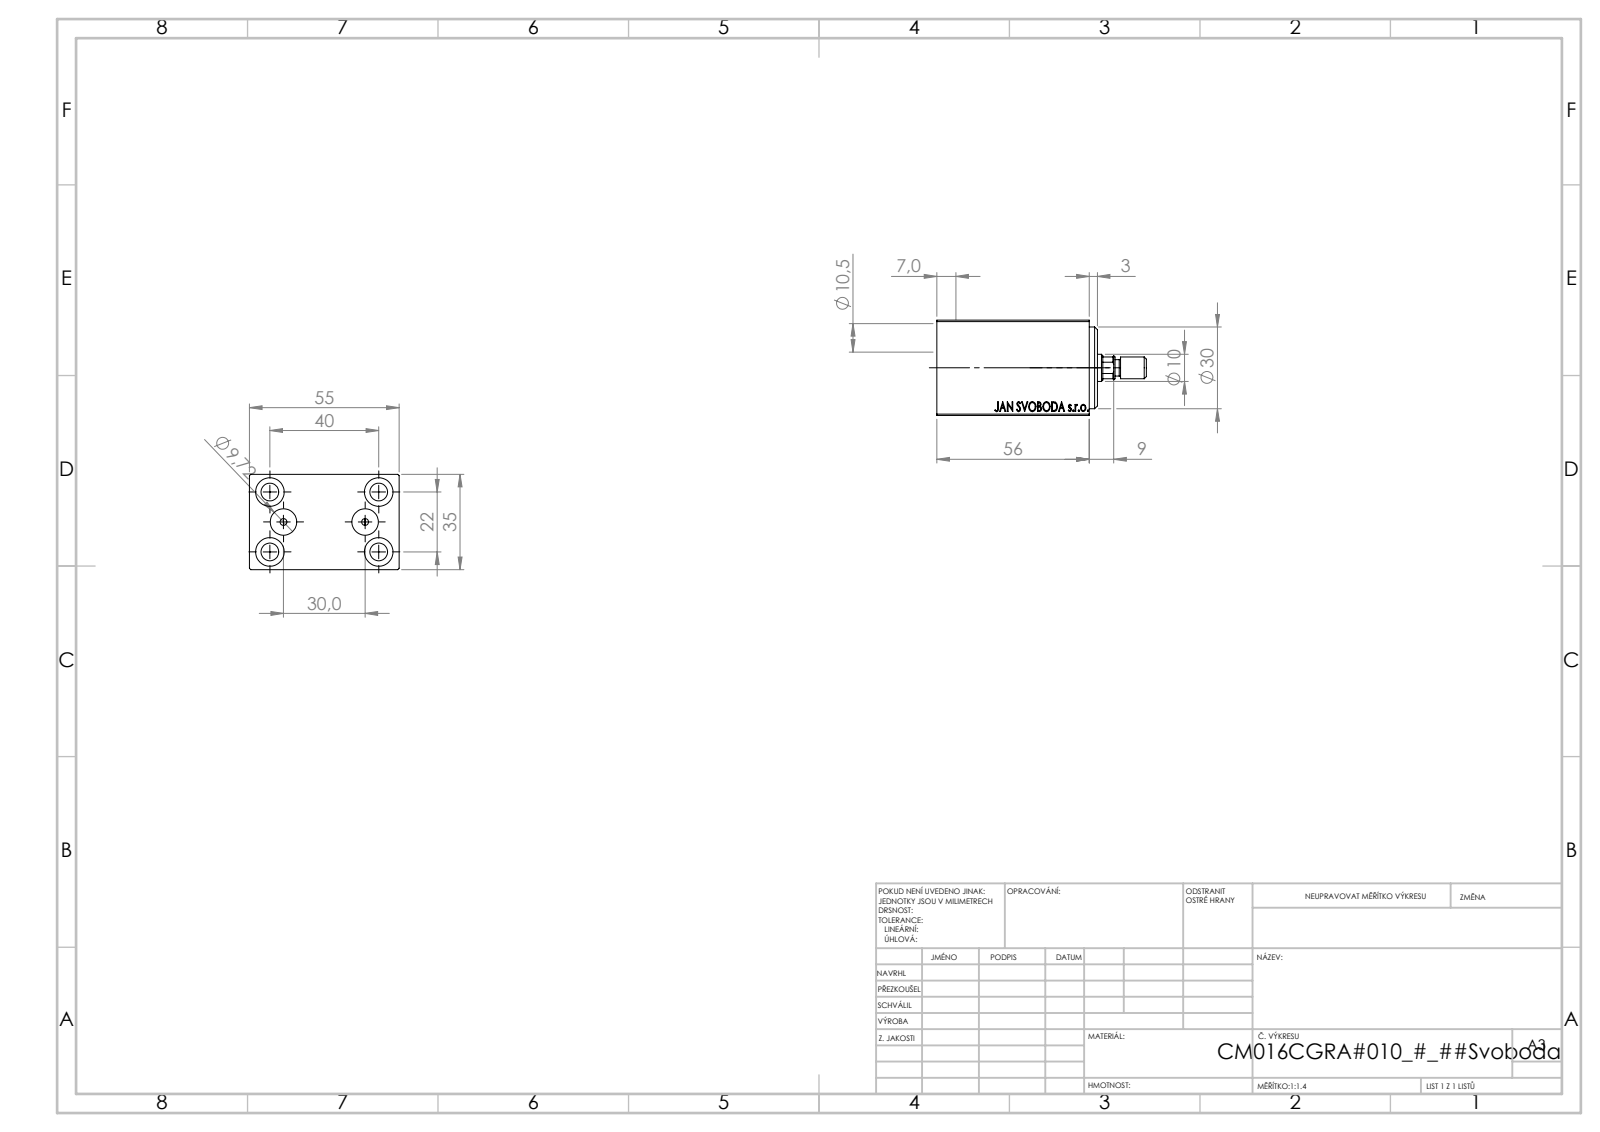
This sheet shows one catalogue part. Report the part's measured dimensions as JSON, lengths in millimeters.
{"part_name": "V450CM_VC_B; V450CM_MALE_METRIC; V450CM_C_Body; V450CM_C_VCP", "step_written_by": "SolidWorks 2019 (CONFIG_CONTROL_DESIGN)", "units": "millimeters", "bodies": {"solids": 4, "faces": 875, "planar": 413, "cylindrical": 62, "other": 400}, "overall_size": [77, 55, 35], "volume_mm3": 96891, "surface_area_mm2": 29058, "round_holes": [[6.5, 4], [10.5, 4], [2.5, 2], [9.72, 2], [4.5, 1], [10, 1], [13.5, 1], [14.5, 1], [16, 1], [18, 1], [30, 1]], "round_bosses_or_shafts": [[8, 1], [6, 1]], "partial_cylinders_radius": [[4.5, 1]], "face_to_face_distances": [35, 55, 5, 51, 56, 2, 3, 49, 46, 8], "hole_center_spacings": [12.08, 22.83, 36.69, 15, 22, 40, 45.65, 30]}
